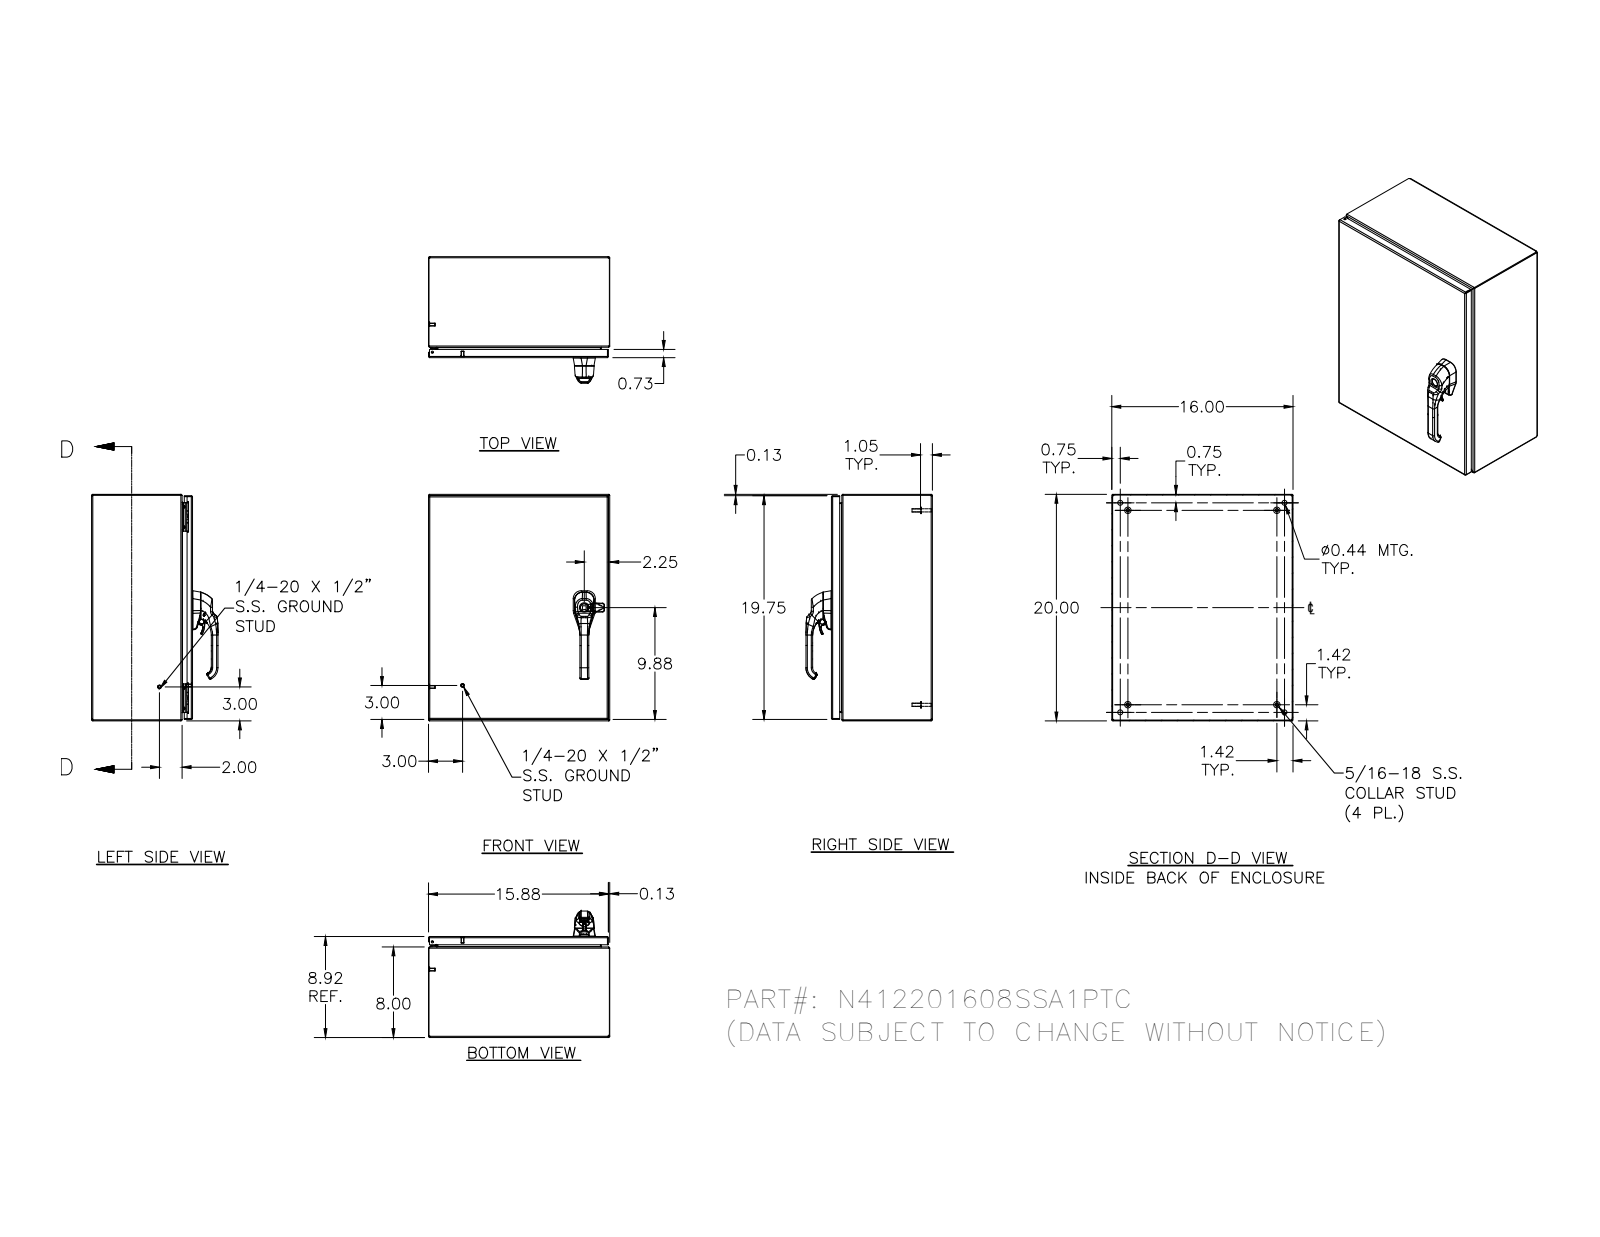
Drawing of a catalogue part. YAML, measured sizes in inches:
part_name: "N412201608SSA1PTC; N412201608SSA1PTCBKP; N4122016SSA1PTCLID; HFW328176 (+8 more)"
step_written_by: "Autodesk Inventor 2012 (AUTOMOTIVE_DESIGN)"
units: inches
bodies: {solids: 41, faces: 2784, planar: 882, cylindrical: 1037, other: 865}
overall_size: [20, 16, 11.166]
volume: 107.9
surface_area: 2836
round_holes:
  - {diameter: 0.188, count: 5}
  - {diameter: 0.093, count: 4}
  - {diameter: 0.152, count: 4}
  - {diameter: 0.167, count: 4}
  - {diameter: 0.172, count: 4}
  - {diameter: 0.437, count: 4}
  - {diameter: 0.213, count: 3}
  - {diameter: 0.281, count: 3}
  - {diameter: 0.156, count: 2}
  - {diameter: 0.315, count: 2}
  - {diameter: 0.402, count: 2}
  - {diameter: 0.413, count: 2}
round_bosses_or_shafts:
  - {diameter: 0.25, count: 10}
  - {diameter: 0.563, count: 4}
  - {diameter: 0.36, count: 4}
  - {diameter: 0.32, count: 4}
  - {diameter: 0.3, count: 4}
  - {diameter: 0.275, count: 4}
  - {diameter: 0.256, count: 4}
  - {diameter: 0.164, count: 4}
partial_cylinders:
  - {radius: 0.02, count: 174}
  - {radius: 0.012, count: 101}
  - {radius: 0.031, count: 30}
  - {radius: 0.05, count: 26}
  - {radius: 0.019, count: 21}
  - {radius: 0.105, count: 20}
  - {radius: 0.016, count: 18}
  - {radius: 0.079, count: 14}
face_to_face_distances: [0.074, 8.843, 15.926, 8.917, 8.769, 19.926, 15.852, 16, 19.852, 20]
hole_center_spacings: [15.996, 0.017, 0.66, 15.283, 16.004, 16.656, 0.019, 0.5]
